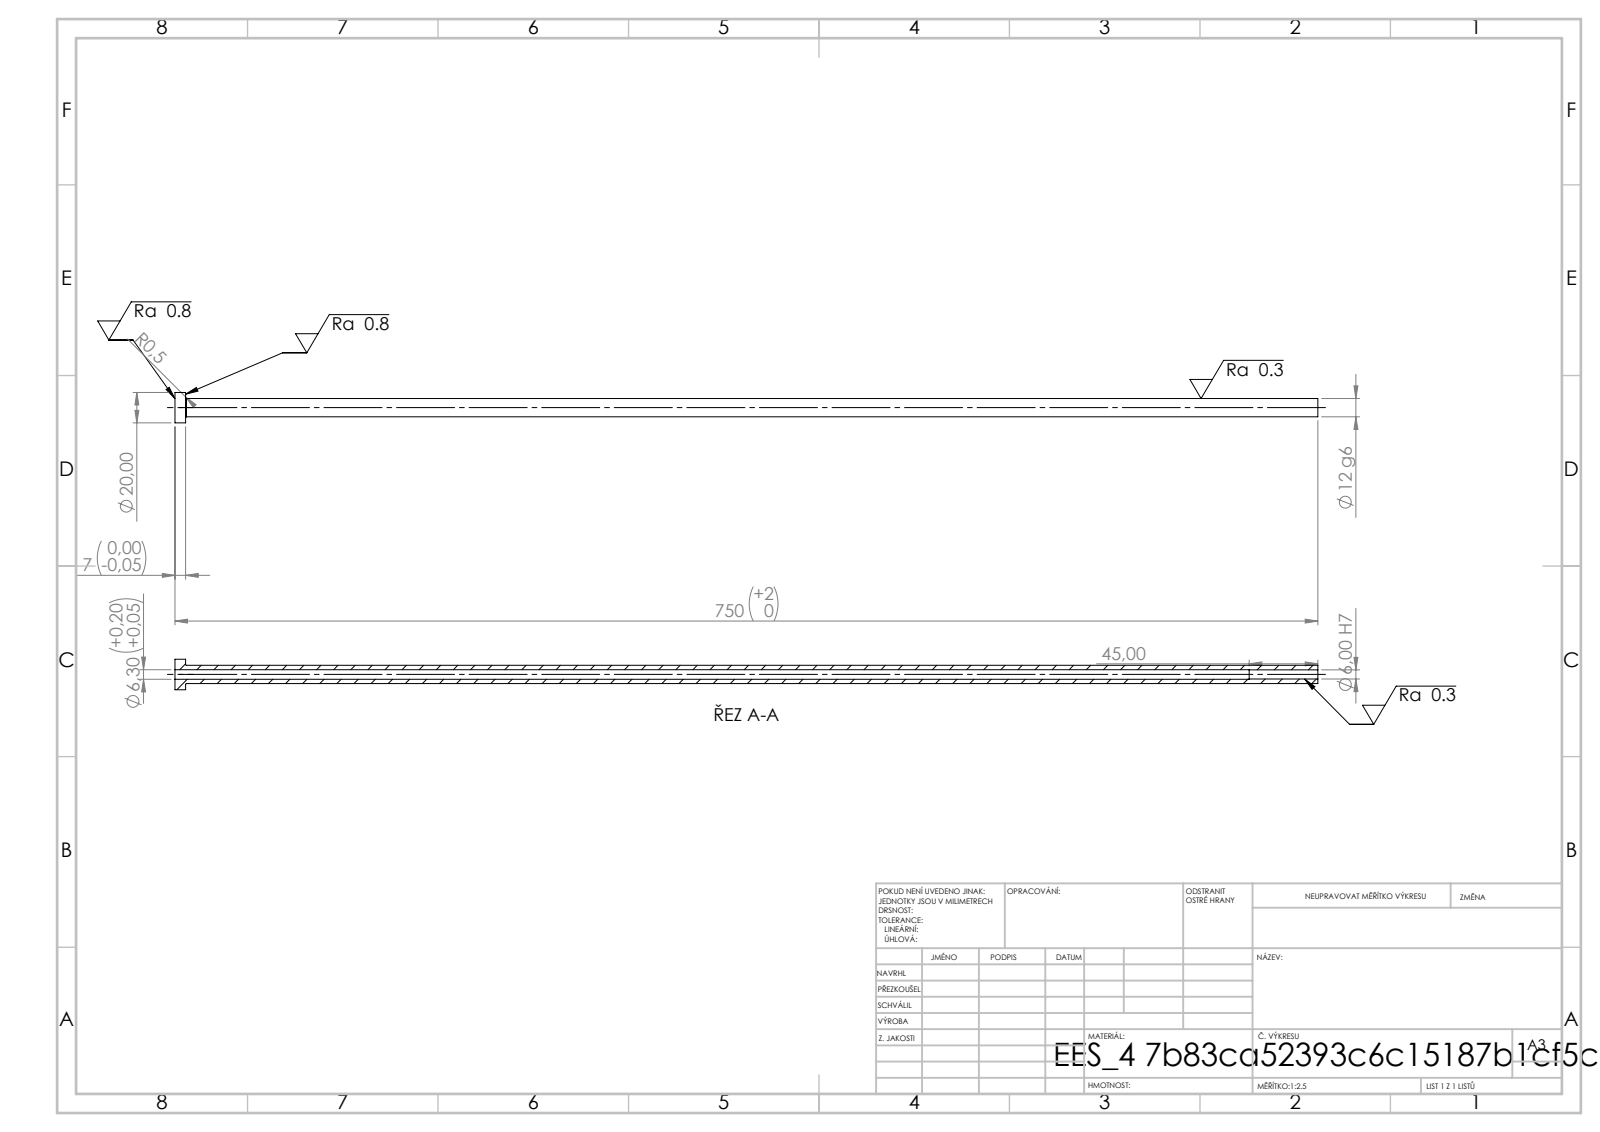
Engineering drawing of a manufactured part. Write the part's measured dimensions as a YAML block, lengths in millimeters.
step_written_by: "SolidWorks 2019 (CONFIG_CONTROL_DESIGN)"
units: millimeters
bodies: {solids: 1, faces: 14, planar: 4, cylindrical: 8, other: 2}
overall_size: [750, 20, 20]
volume: 62984
surface_area: 43816
round_holes:
  - {diameter: 6, count: 1}
  - {diameter: 6.3, count: 1}
round_bosses_or_shafts:
  - {diameter: 20, count: 1}
  - {diameter: 12, count: 1}
face_to_face_distances: [7, 750, 743, 705, 698, 45]
